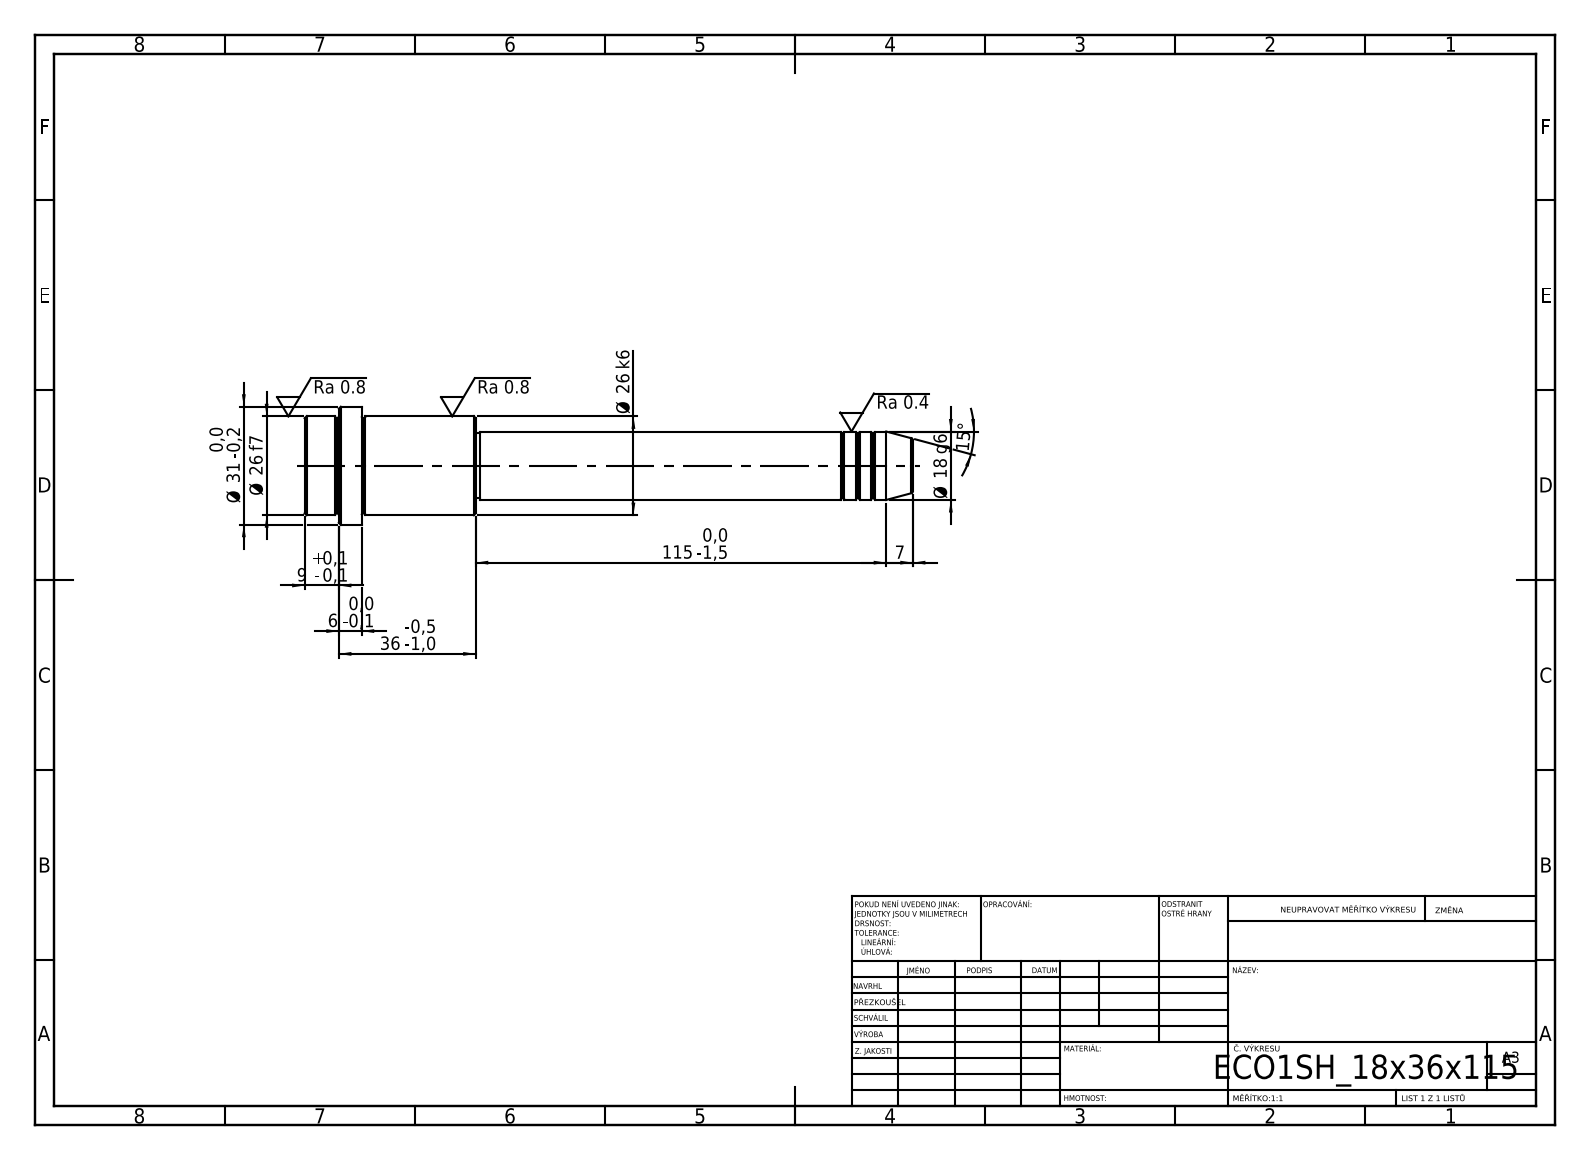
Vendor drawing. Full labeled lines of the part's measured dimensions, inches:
STEP written by: SolidWorks 2019 (CONFIG_CONTROL_DESIGN)
Units: inches
Bodies: 1 solid, 52 faces (6 planar, 16 cylindrical, 30 other)
Overall size (bounding box): 6.299 × 1.22 × 1.22
Volume: 3.293 in³ · Surface area: 18.29 in²
Round bosses / shafts (diameter × count): ⌀1.22 ×1, ⌀1.024 ×1, ⌀0.709 ×1, ⌀0.669 ×1
Main face-to-face distances: 1.772, 1.181, 0.591, 1.417, 0.236, 0.354, 4.528, 5.709, 5.945, 6.299
